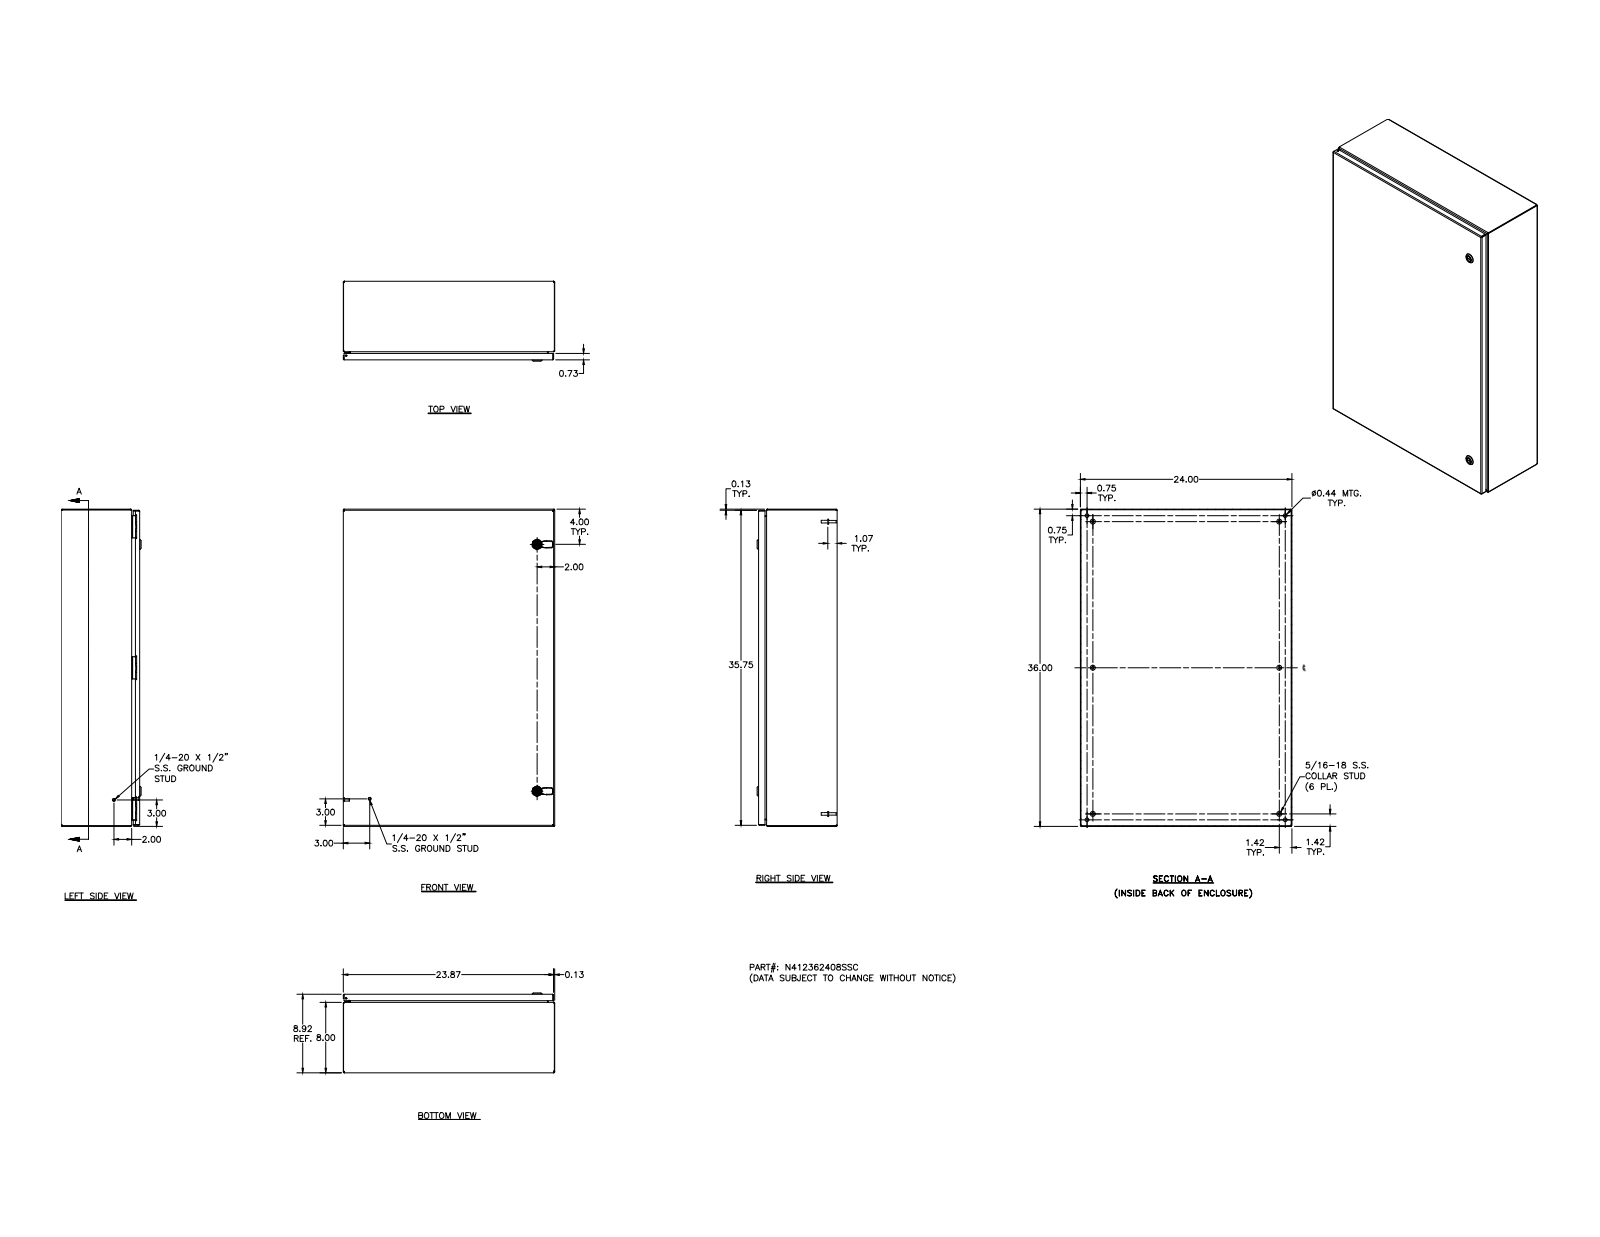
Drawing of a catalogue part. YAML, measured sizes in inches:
part_name: "N412362408SSC; N412362408SSCBKP; 388151; N4123624SSCLID (+8 more)"
step_written_by: "Autodesk Inventor 2011 (AUTOMOTIVE_DESIGN)"
units: inches
bodies: {solids: 53, faces: 2118, planar: 831, cylindrical: 778, other: 509}
overall_size: [36, 24, 9.075]
volume: 217.8
surface_area: 5909
round_holes:
  - {diameter: 0.188, count: 7}
  - {diameter: 0.093, count: 6}
  - {diameter: 0.152, count: 6}
  - {diameter: 0.167, count: 6}
  - {diameter: 0.172, count: 6}
  - {diameter: 0.437, count: 4}
  - {diameter: 0.156, count: 3}
  - {diameter: 0.197, count: 2}
  - {diameter: 0.315, count: 2}
  - {diameter: 0.394, count: 2}
  - {diameter: 0.402, count: 2}
  - {diameter: 0.634, count: 2}
round_bosses_or_shafts:
  - {diameter: 0.25, count: 14}
  - {diameter: 0.563, count: 6}
  - {diameter: 0.36, count: 6}
  - {diameter: 0.32, count: 6}
  - {diameter: 0.3, count: 6}
  - {diameter: 0.275, count: 6}
  - {diameter: 0.256, count: 6}
  - {diameter: 0.164, count: 6}
partial_cylinders:
  - {radius: 0.05, count: 38}
  - {radius: 0.031, count: 34}
  - {radius: 0.016, count: 26}
  - {radius: 0.125, count: 21}
  - {radius: 0.105, count: 20}
  - {radius: 0.02, count: 15}
  - {radius: 0.032, count: 12}
  - {radius: 0.07, count: 8}
face_to_face_distances: [0.074, 8.843, 8.769, 8.917, 23.926, 35.926, 23.852, 24, 36, 35.852]
hole_center_spacings: [16.004, 32, 15.996, 0.017, 0.66, 15.992, 16, 16.008]
